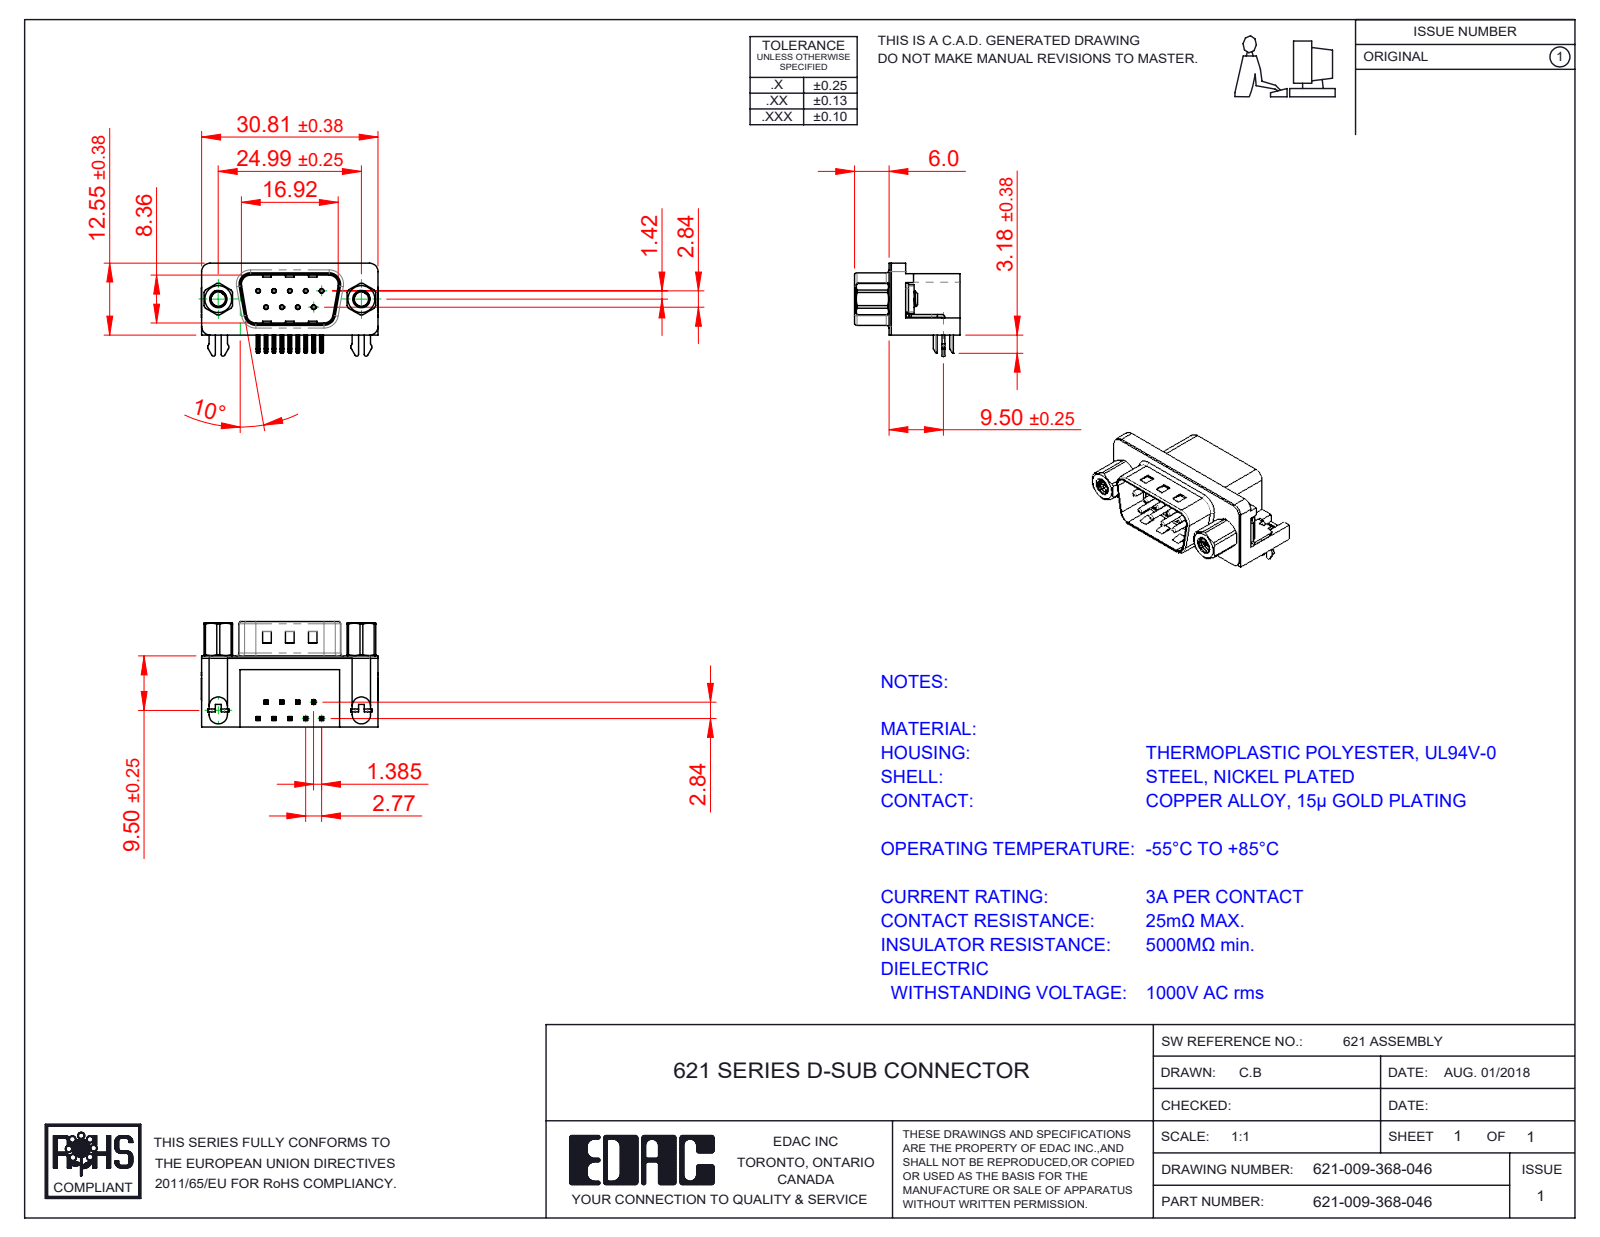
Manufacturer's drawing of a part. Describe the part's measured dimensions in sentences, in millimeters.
The part is named "621 Shell_9 Socket; 621 M3 Hex Standoff 5; 621 Contact Top; 621 4 Prong Board Lock (+4 more)". Its 3-D file was written by "SolidWorks 2016 (CONFIG_CONTROL_DESIGN)". It is 17 solids with 1259 faces: 637 planar, 417 cylindrical and 205 other. Overall it measures 30.89 by 18.4 by 16.25 millimeters. Its volume is 3 495 cubic millimeters and its surface area 5 028 square millimeters. Round holes: 9 of diameter 0.35, 9 of diameter 0.8, 2 of diameter 2, 2 of diameter 2.5, 2 of diameter 4, 2 of diameter 4.8, 2 of diameter 5. Round bosses or shafts: 9 of diameter 0.75, 4 of diameter 3, 2 of diameter 4.9, 2 of diameter 4.75, 2 of diameter 3.9. Partial cylindrical surfaces (rounded edges, fillets, slot ends): 48 of radius 0.25, 18 of radius 0.12, 16 of radius 1, 9 of radius 0.5, 8 of radius 1.5, 8 of radius 1.6, 4 of radius 0.9, 4 of radius 2. The main face-to-face distances are 0.4, 12, 12.4, 10.35, 9.5, 2.5, 2.9, 2.1, 0.35, 10.7. The hole center spacings are 3.16, 2.77, 5.54, 5.03, 5.04, 8.31, 7.48, 7.49.
